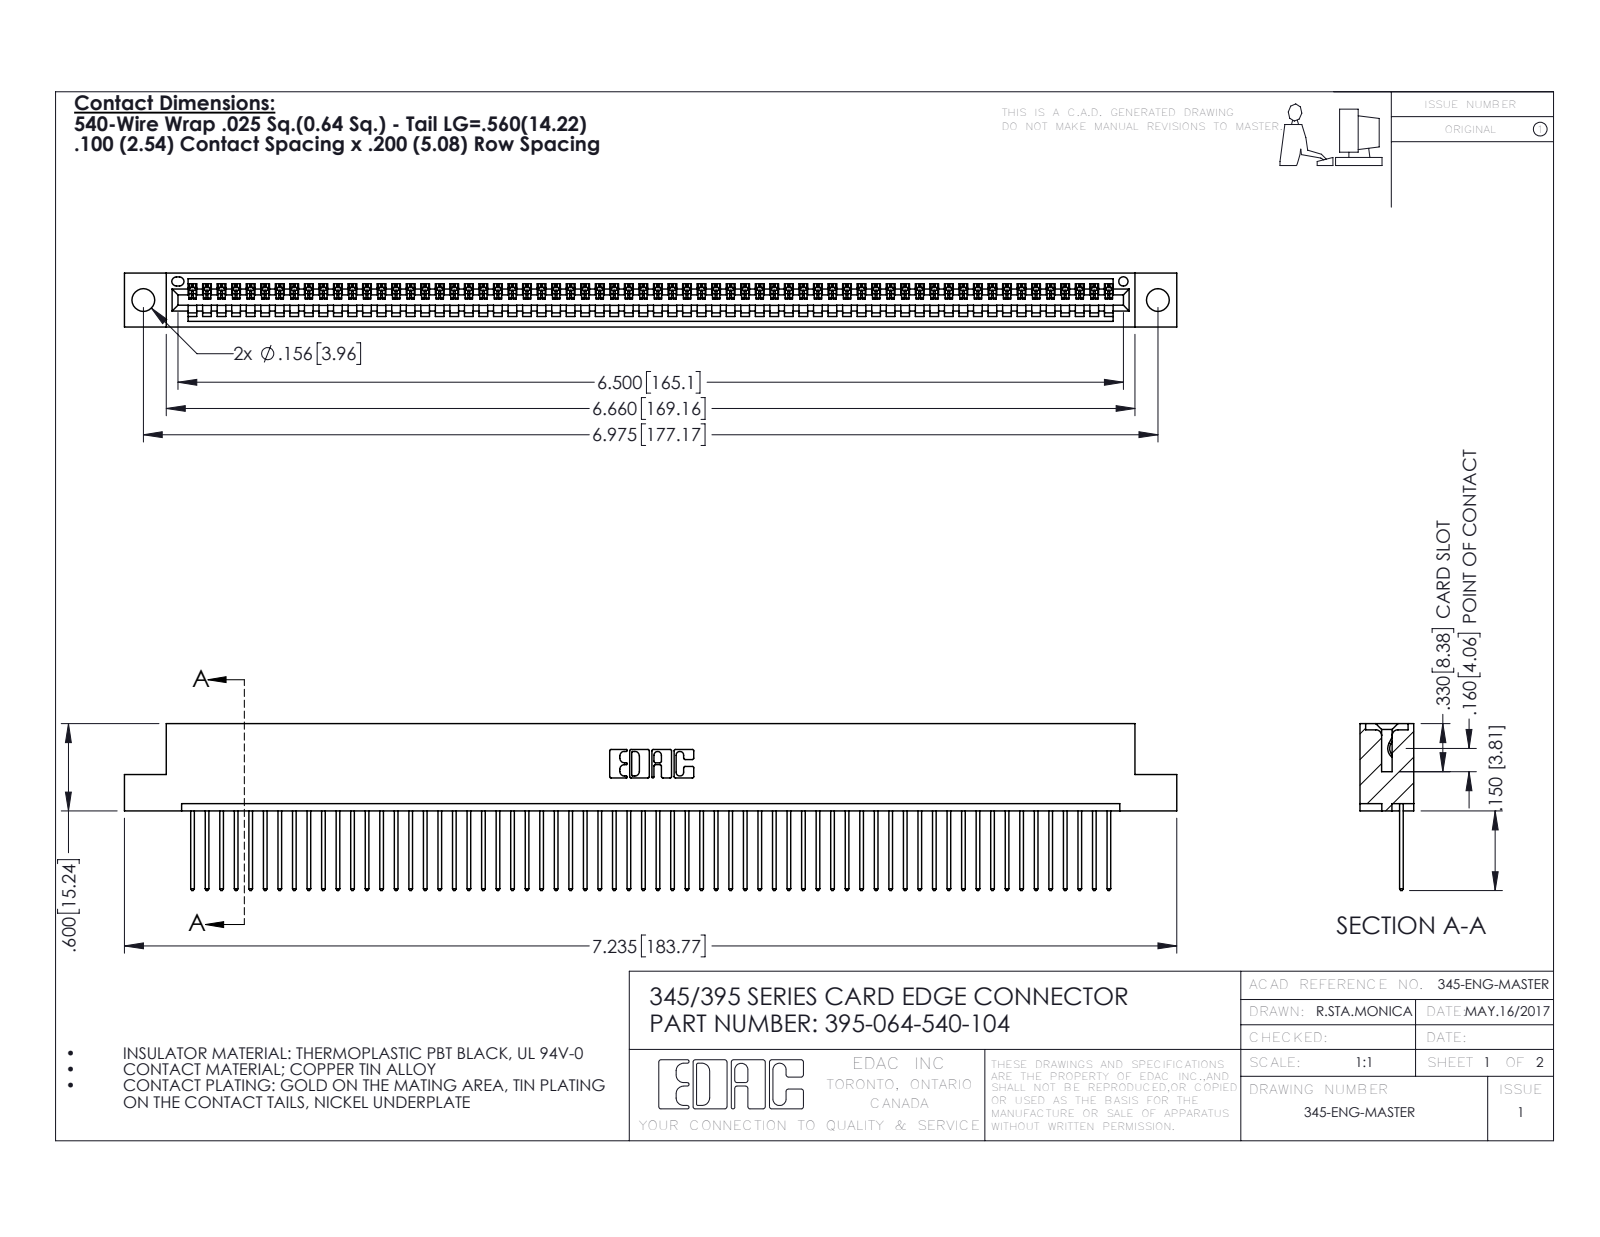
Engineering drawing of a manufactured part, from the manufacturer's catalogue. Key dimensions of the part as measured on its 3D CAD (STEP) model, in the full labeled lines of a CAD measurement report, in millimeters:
Part name (STEP PRODUCT): 345 Part_Flush Mounting Lugs - 0.156 Dia-TH; 345-292-001_345-293-140; 395-064-540-104
STEP written by: SolidWorks 2016 (CONFIG_CONTROL_DESIGN)
Units: millimetres
Bodies: 65 solids, 3838 faces (2640 planar, 1198 cylindrical, 0 other)
Overall size (bounding box): 183.8 × 29.1 × 9.4
Volume: 17 630 mm³ · Surface area: 24 170 mm²
Round holes (diameter × count): ⌀4 ×2, ⌀1.6 ×1
Partial cylindrical surfaces — rounded edges, fillets, slot ends (radius × count): R0.2 ×128, R0.3 ×128, R0.3 ×22, R0.2 ×6, R0.8 ×6, R0.7 ×3, R0.8 ×2, R1 ×2
Main face-to-face distances: 7.6, 1.8, 9.4, 2.5, 6.9, 0.6, 5.1, 5.7, 3.8, 1.8
Hole centre spacings: 6.9, 171.2, 177.2
